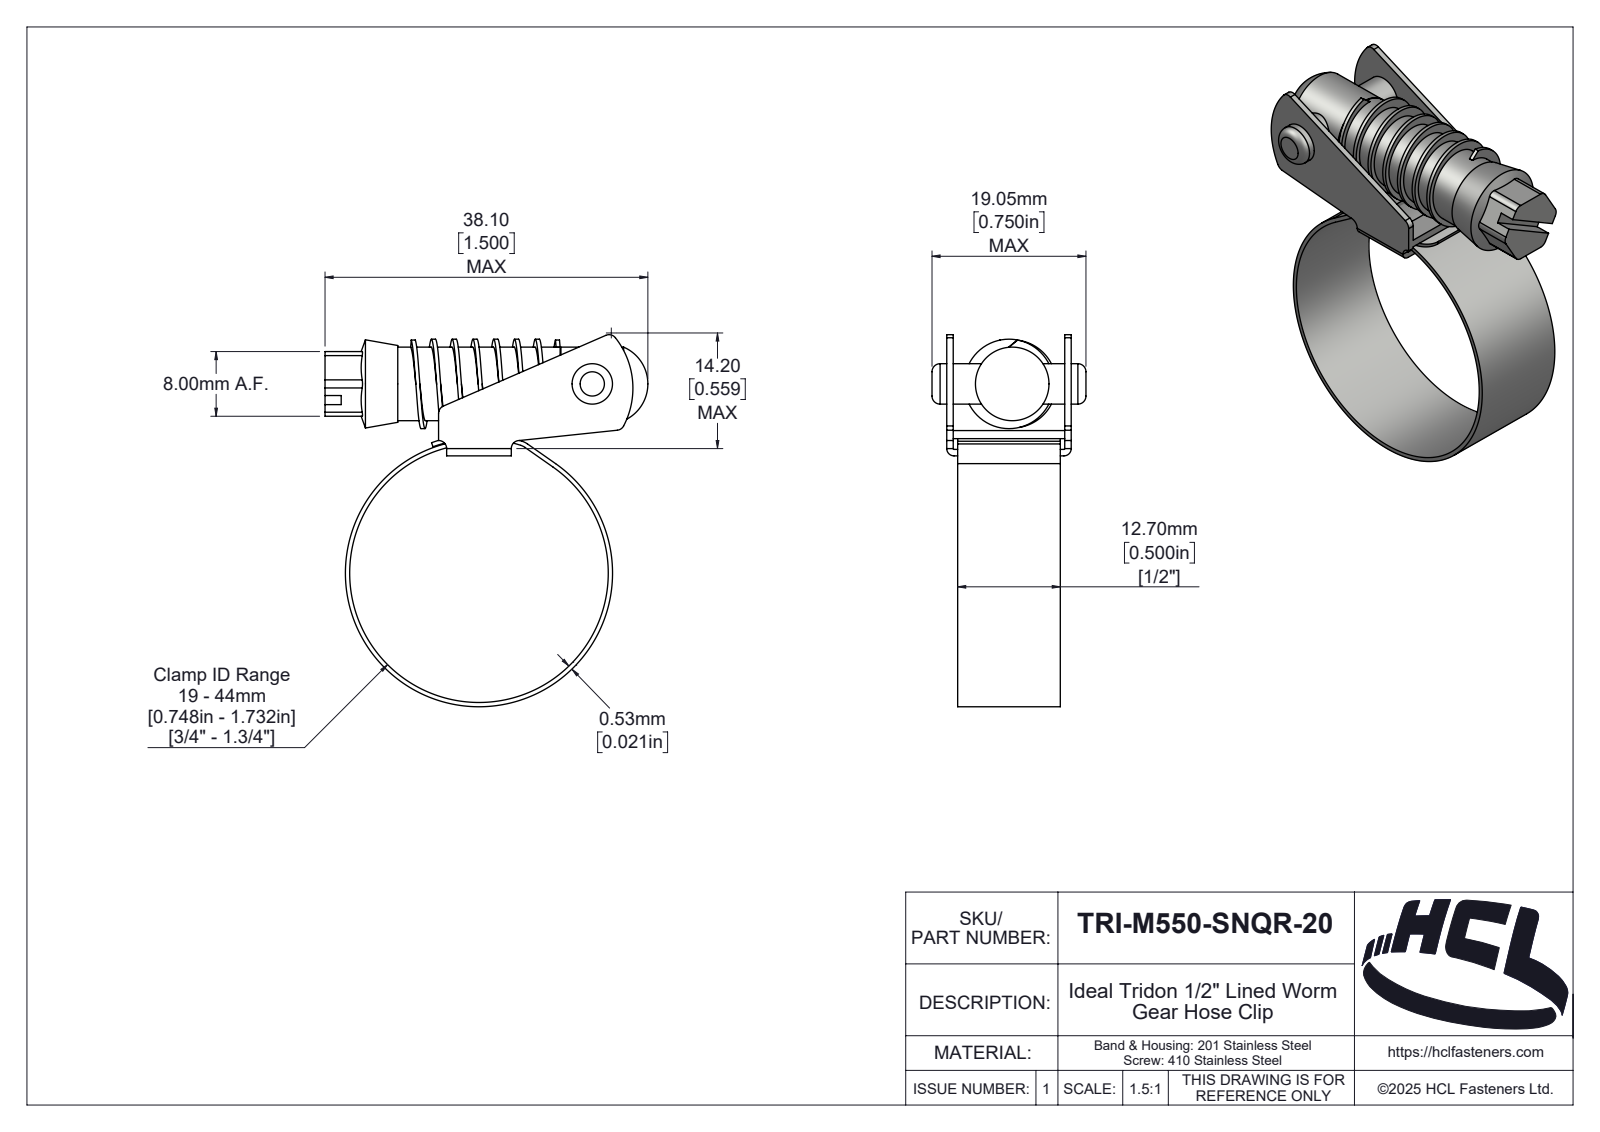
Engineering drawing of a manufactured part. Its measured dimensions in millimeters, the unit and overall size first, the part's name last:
Units: millimetres
Overall size (bounding box): 58.02 × 45.06 × 19.05
Round holes (diameter × count): ⌀5 ×1, ⌀44 ×1
Round bosses / shafts (diameter × count): ⌀45.06 ×1, ⌀9.1 ×1
Partial cylindrical surfaces — rounded edges, fillets, slot ends (radius × count): R1 ×11, R0.1 ×2, R0.9 ×2, R3 ×2, R0.46 ×1, R1.89 ×1, R2 ×1, R2.35 ×1
Main face-to-face distances: 0.8, 14.6, 15.4, 13.8, 1.35, 14.05, 0.55, 13.25, 1, 2.13
Hole centre spacings: 32.57
Volume: 4 176 mm³ · Surface area: 7 504 mm²
Bodies: 5 solids, 222 faces (44 planar, 112 cylindrical, 66 other)
Part name (STEP PRODUCT): TRI-M550-SNQR-20
STEP written by: SolidWorks 2025 (AUTOMOTIVE_DESIGN)
